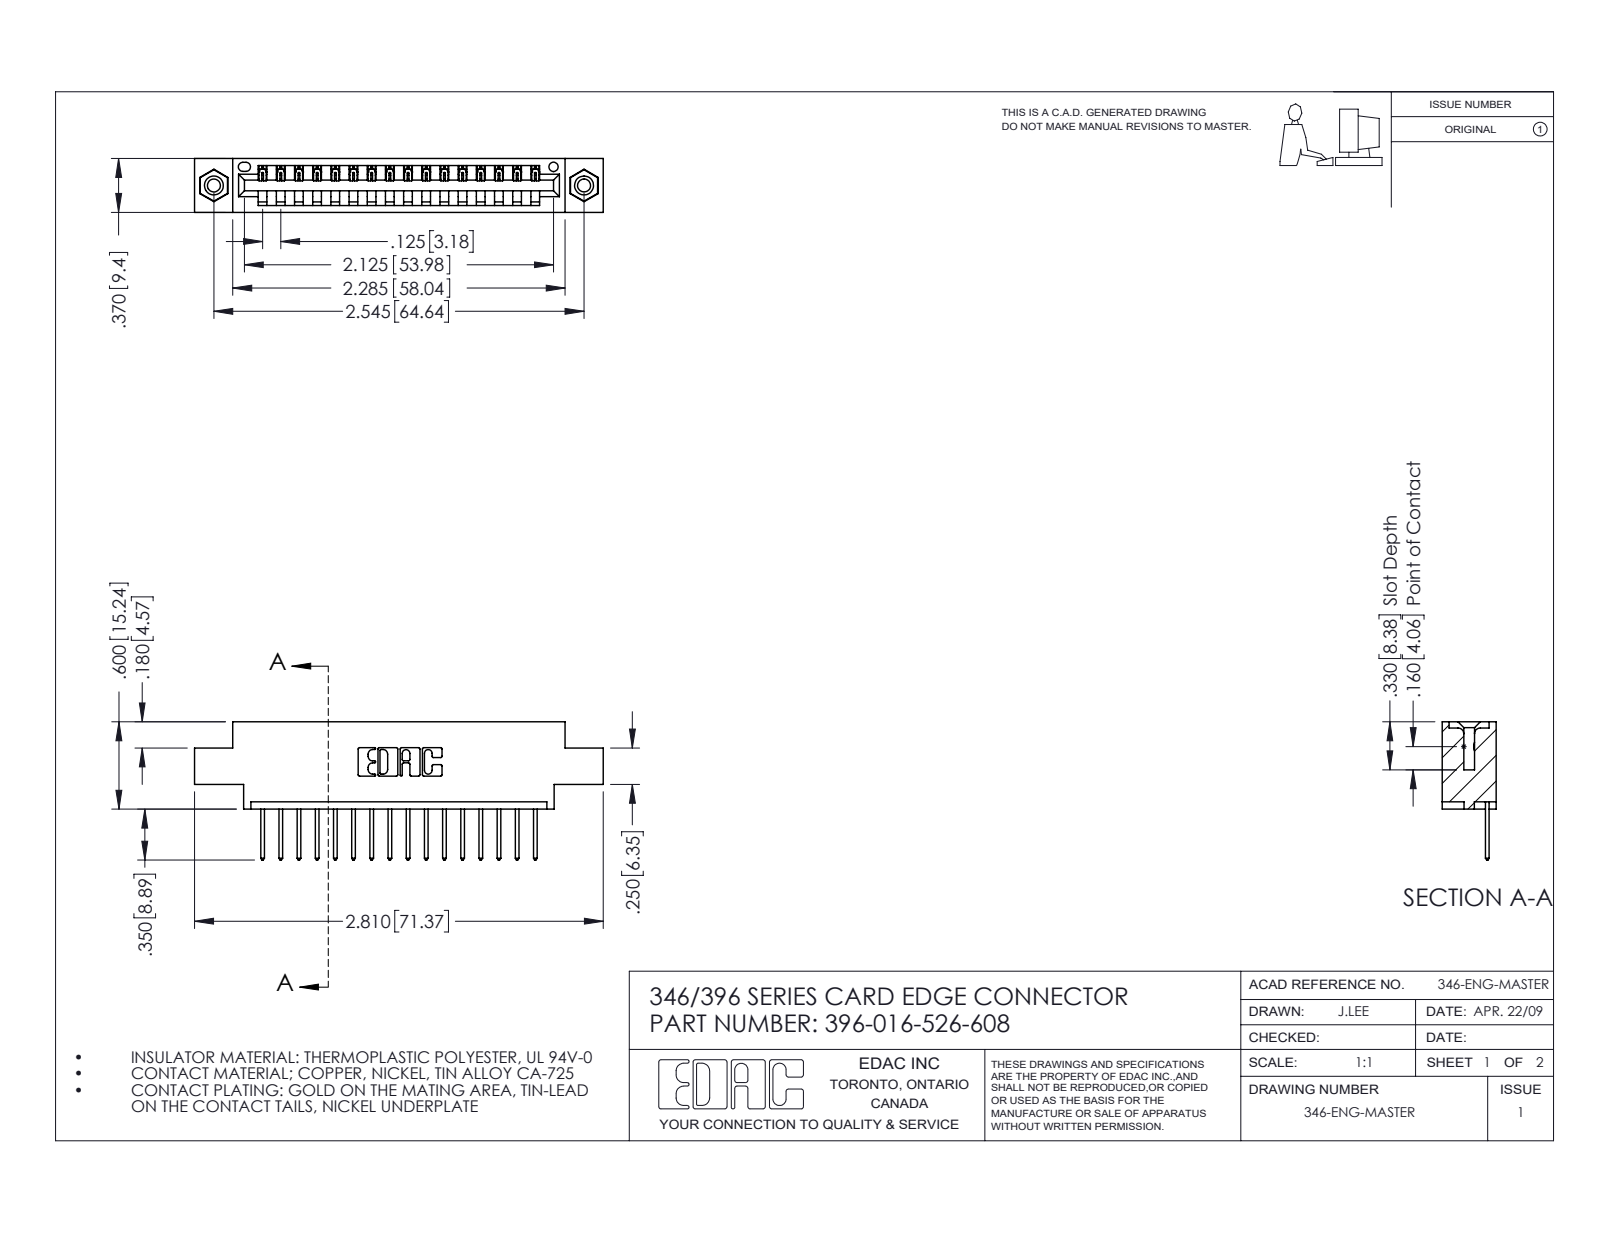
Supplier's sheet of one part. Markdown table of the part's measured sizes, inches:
| quantity | value |
| --- | --- |
| part name | 396-016-526-608; 346 Part_0.170 Offset - 0.156 Dia-TI; 345-250-001_345-250-003-102; 345-292-001_345-293-126 |
| STEP written by | SolidWorks 2016 (CONFIG_CONTROL_DESIGN) |
| units | inches |
| bodies | 19 solids, 1114 faces (752 planar, 346 cylindrical, 16 other) |
| overall size | 2.81 × 0.95 × 0.37 |
| volume | 0.395 in³ |
| surface area | 12.38 in² |
| round holes (diameter × count) | 0.089 × 2, 0.125 × 2, 0.156 × 2, 0.064 × 1 |
| round bosses / shafts (diameter × count) | 0.155 × 2 |
| partial cylindrical surfaces (radius × count) | 0.006 × 32, 0.01 × 32, 0.01 × 22, 0.007 × 6, 0.031 × 6, 0.026 × 3, 0.031 × 2, 0.04 × 2 |
| main face-to-face distances | 0.048, 0.322, 0.37, 0.25, 0.072, 0.298, 0.025, 0.222, 0.148, 0.1 |
| hole center spacings | 0.246, 2.338, 2.545 |
